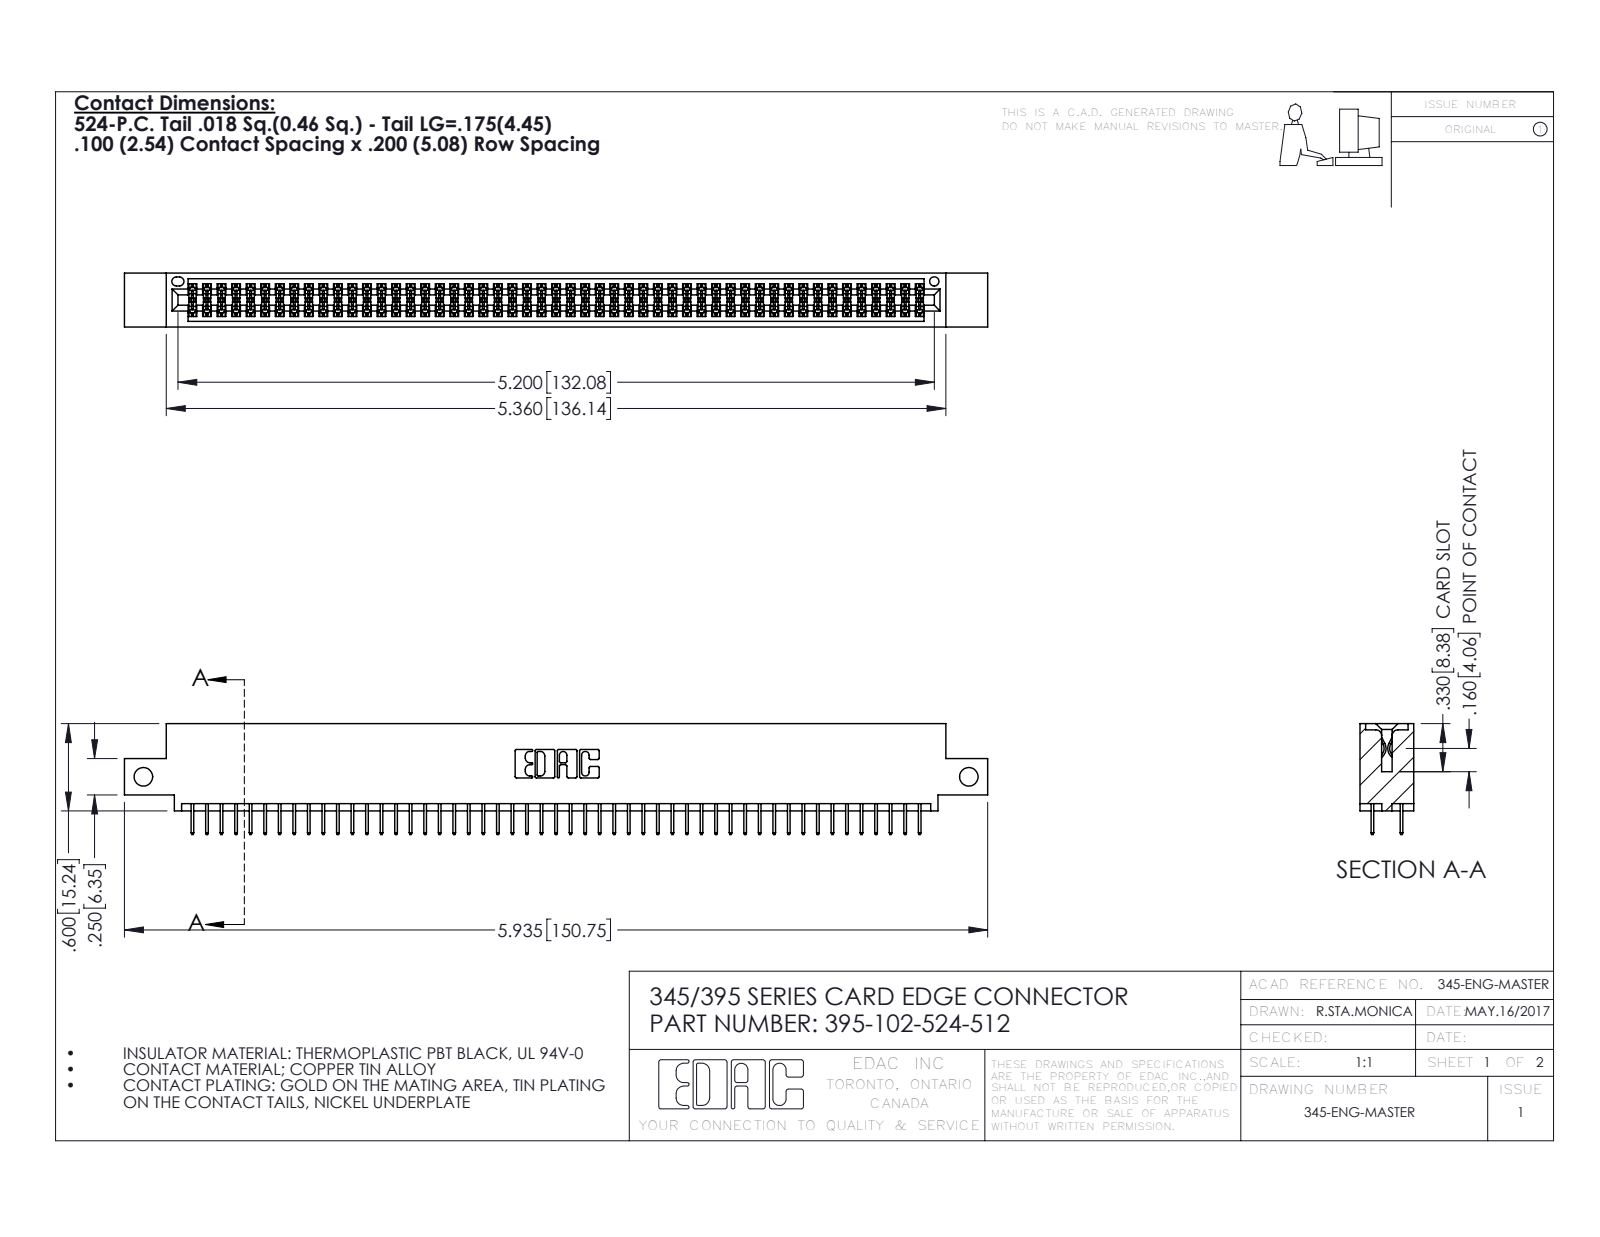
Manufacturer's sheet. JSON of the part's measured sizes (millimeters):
{"part_name": "345 Part_0.110 Offset - Side Mount; 395-102-524-512; 345-292-001_345-293-124", "step_written_by": "SolidWorks 2016 (CONFIG_CONTROL_DESIGN)", "units": "millimeters", "bodies": {"solids": 103, "faces": 5638, "planar": 4062, "cylindrical": 1576, "other": 0}, "overall_size": [150.7, 19.4, 9.4], "volume_mm3": 14400, "surface_area_mm2": 21030, "round_holes": [[3.3, 2], [1.6, 1]], "partial_cylinders_radius": [[0.2, 153], [0.3, 22], [0.2, 6], [0.8, 6], [0.7, 3], [0.4, 2], [0.5, 2], [0.6, 2]], "face_to_face_distances": [1.8, 7.6, 5.1, 9.4, 2.5, 6.9, 0.6, 5.7, 1.8, 4.4], "hole_center_spacings": [144.1]}
